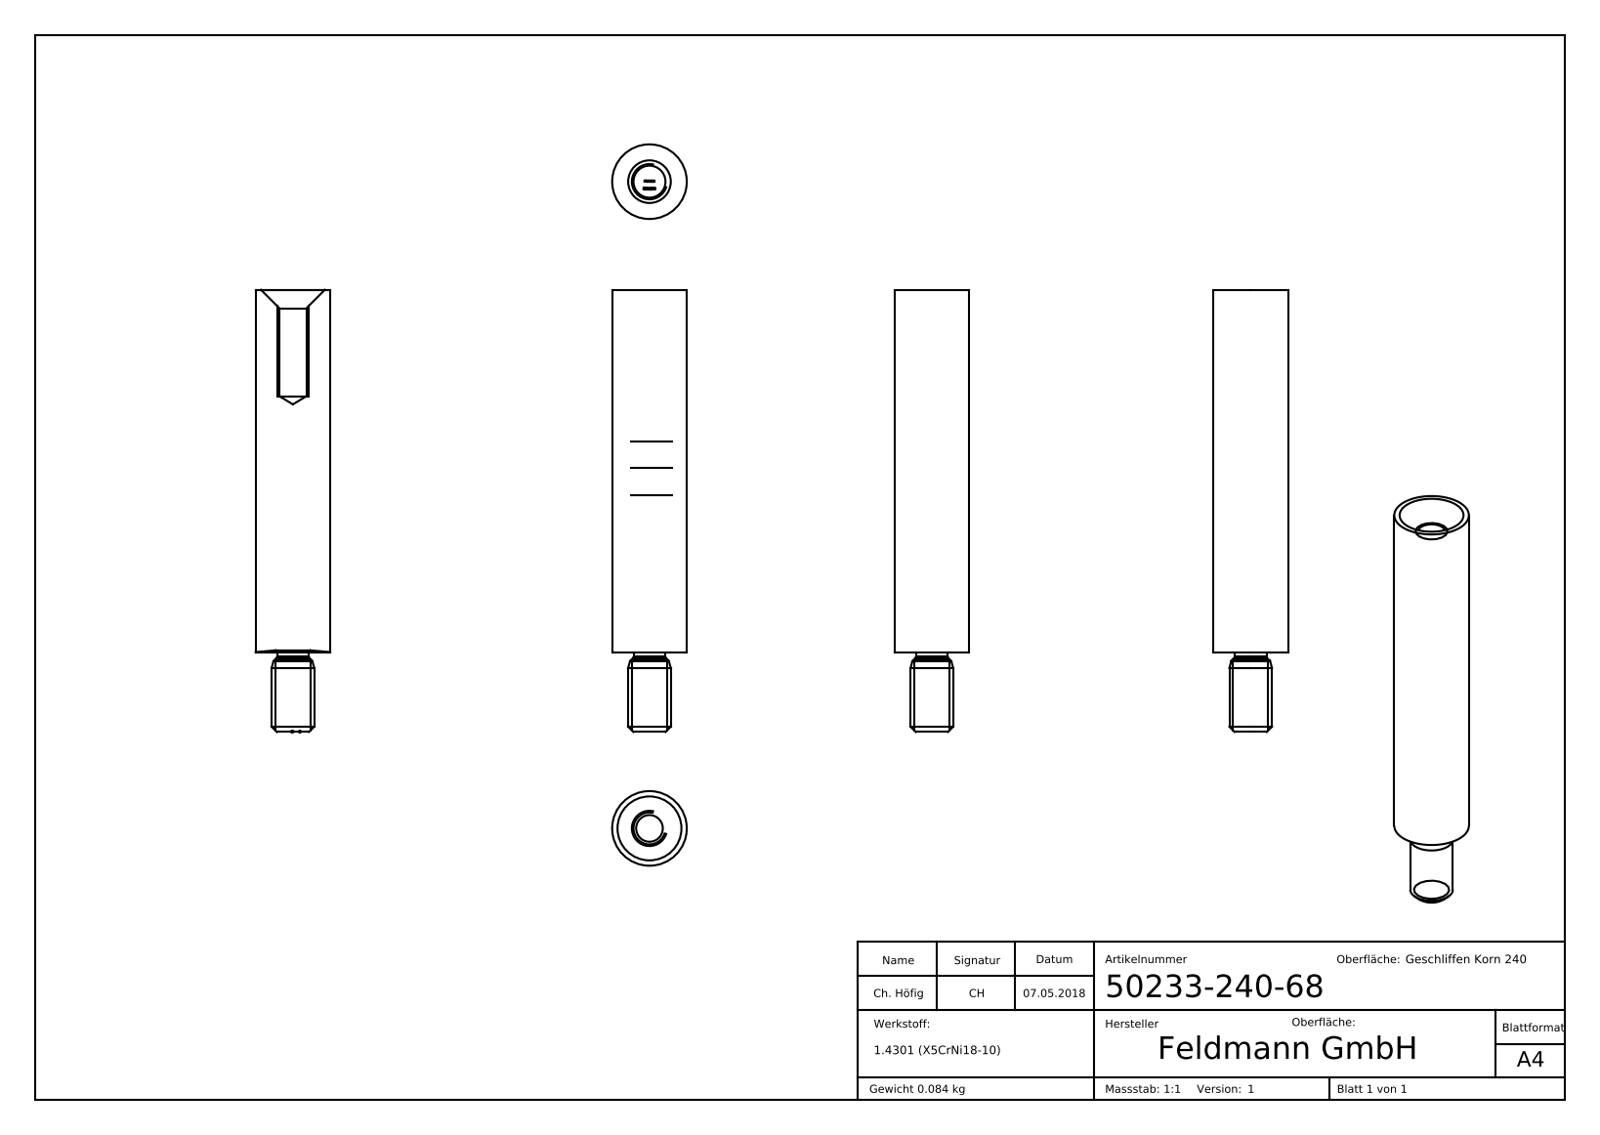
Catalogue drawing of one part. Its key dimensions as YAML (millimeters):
part_name: "50233-240-68"
step_written_by: "SolidWorks 2015 (CONFIG_CONTROL_DESIGN)"
units: millimeters
bodies: {solids: 1, faces: 30, planar: 2, cylindrical: 8, other: 20}
overall_size: [83, 14, 14]
volume: 10609
surface_area: 3983
round_holes:
  - {diameter: 5, count: 1}
round_bosses_or_shafts:
  - {diameter: 14, count: 1}
  - {diameter: 8, count: 1}
  - {diameter: 6, count: 1}
face_to_face_distances: [83]
